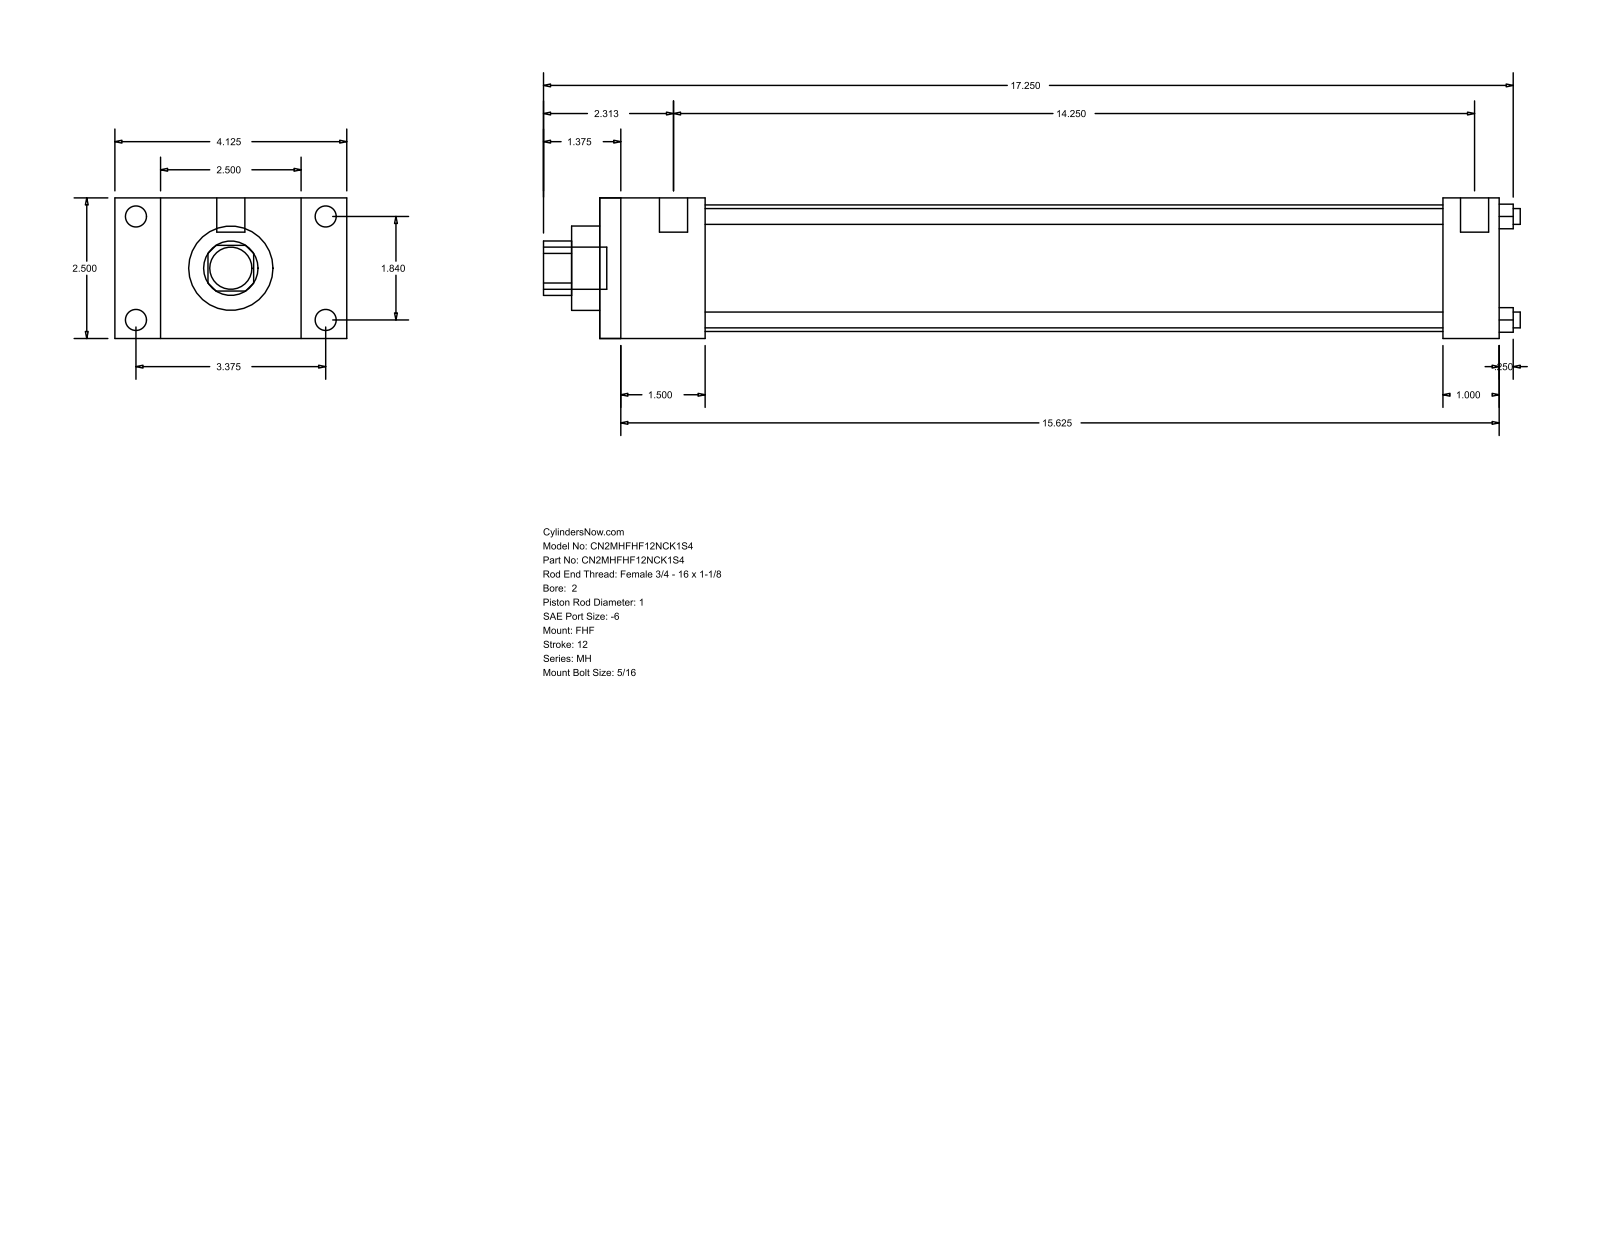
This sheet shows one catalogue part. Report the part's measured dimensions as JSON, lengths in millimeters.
{"part_name": "MH_FHF__0200_1", "step_written_by": "GSSL Pune (CONFIG_CONTROL_DESIGN)", "units": "millimeters", "bodies": {"solids": 0, "faces": 88, "planar": 60, "cylindrical": 28, "other": 0}, "overall_size": [441.32, 104.78, 63.5], "round_holes": [[7.14, 4], [25.4, 1], [38.1, 1], [57.15, 1]], "round_bosses_or_shafts": [[9.53, 4], [5.56, 4], [12.7, 2], [19.05, 1]], "partial_cylinders_radius": [[12.29, 1]], "face_to_face_distances": [63.5, 406.4, 47.63, 358.77, 20.64, 84.14, 104.78, 25.4, 381, 333.37], "hole_center_spacings": [33.05, 46.74, 66.1]}
